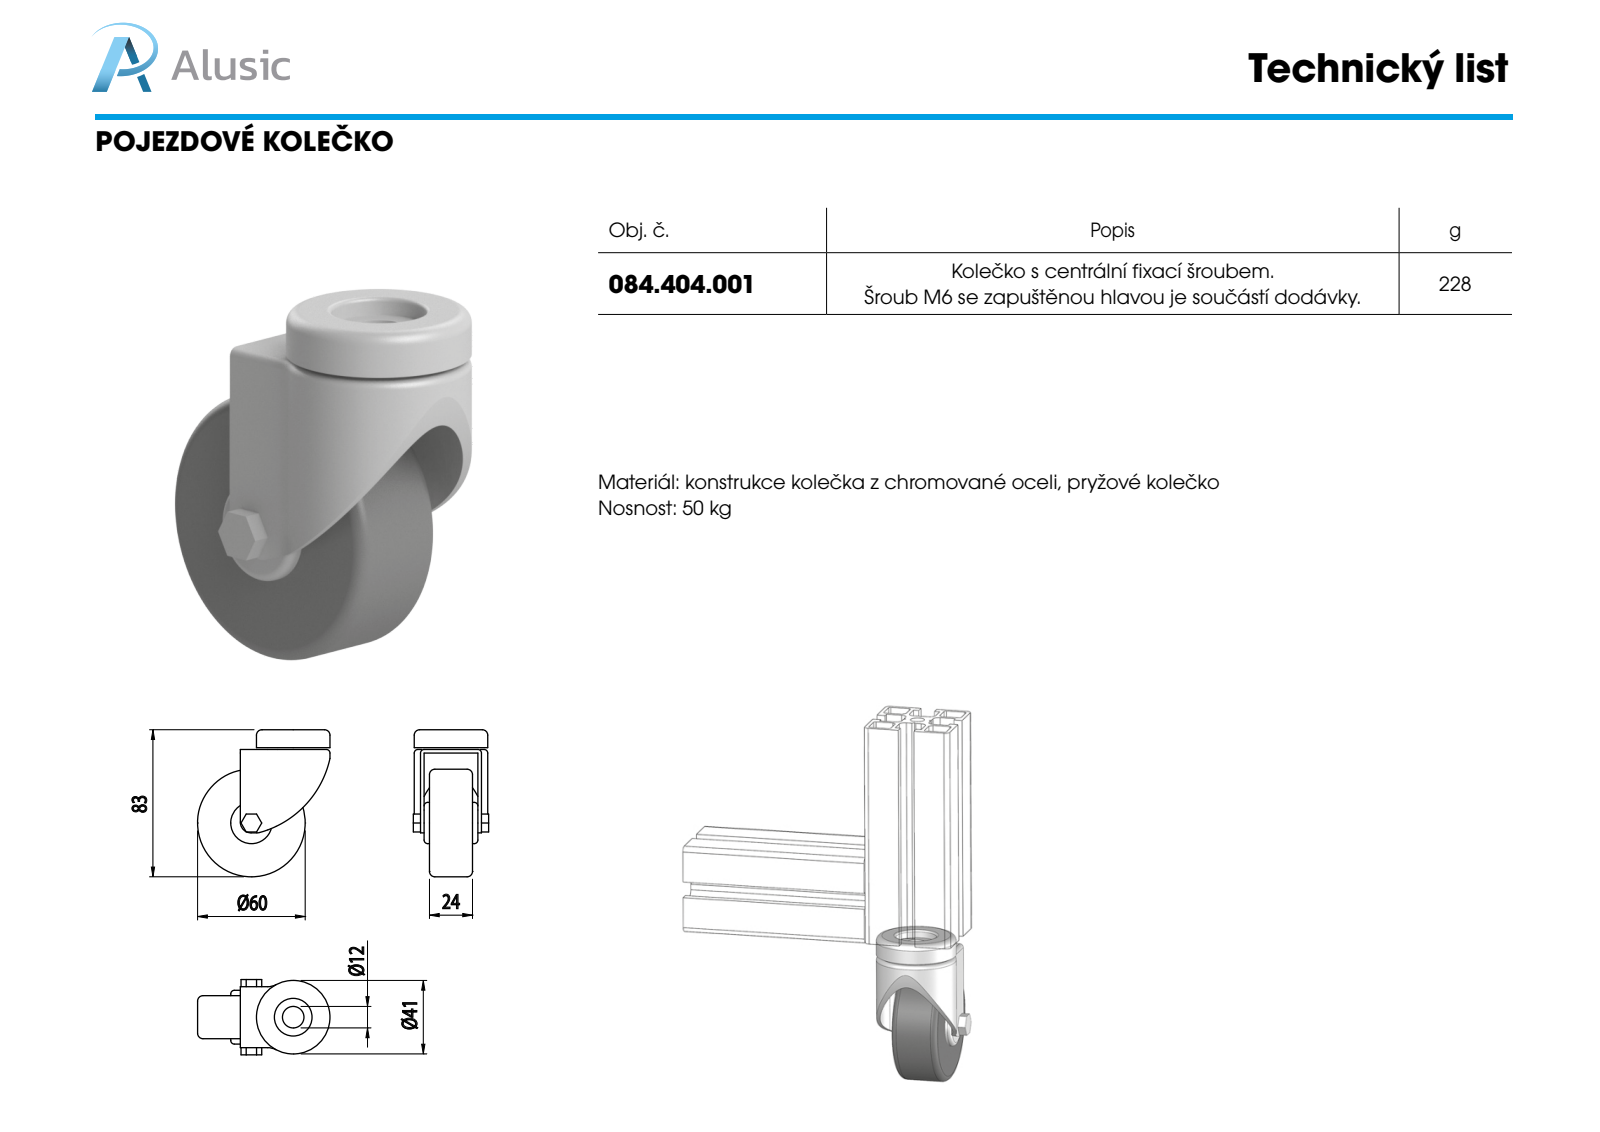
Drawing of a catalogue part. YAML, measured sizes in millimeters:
part_name: "084.404.001"
step_written_by: "SolidWorks 2011 (CONFIG_CONTROL_DESIGN)"
units: millimeters
bodies: {solids: 6, faces: 84, planar: 34, cylindrical: 31, other: 19}
overall_size: [82, 73.84, 42]
volume: 93420
surface_area: 29662
round_holes:
  - {diameter: 12, count: 1}
  - {diameter: 21, count: 1}
  - {diameter: 39, count: 1}
round_bosses_or_shafts:
  - {diameter: 23, count: 2}
  - {diameter: 60, count: 1}
  - {diameter: 41, count: 1}
partial_cylinders:
  - {radius: 2, count: 2}
  - {radius: 6, count: 2}
  - {radius: 10, count: 2}
  - {radius: 12, count: 2}
  - {radius: 18.5, count: 1}
  - {radius: 55, count: 1}
face_to_face_distances: [2, 24, 3, 5, 27, 29, 32, 30, 1, 10]
